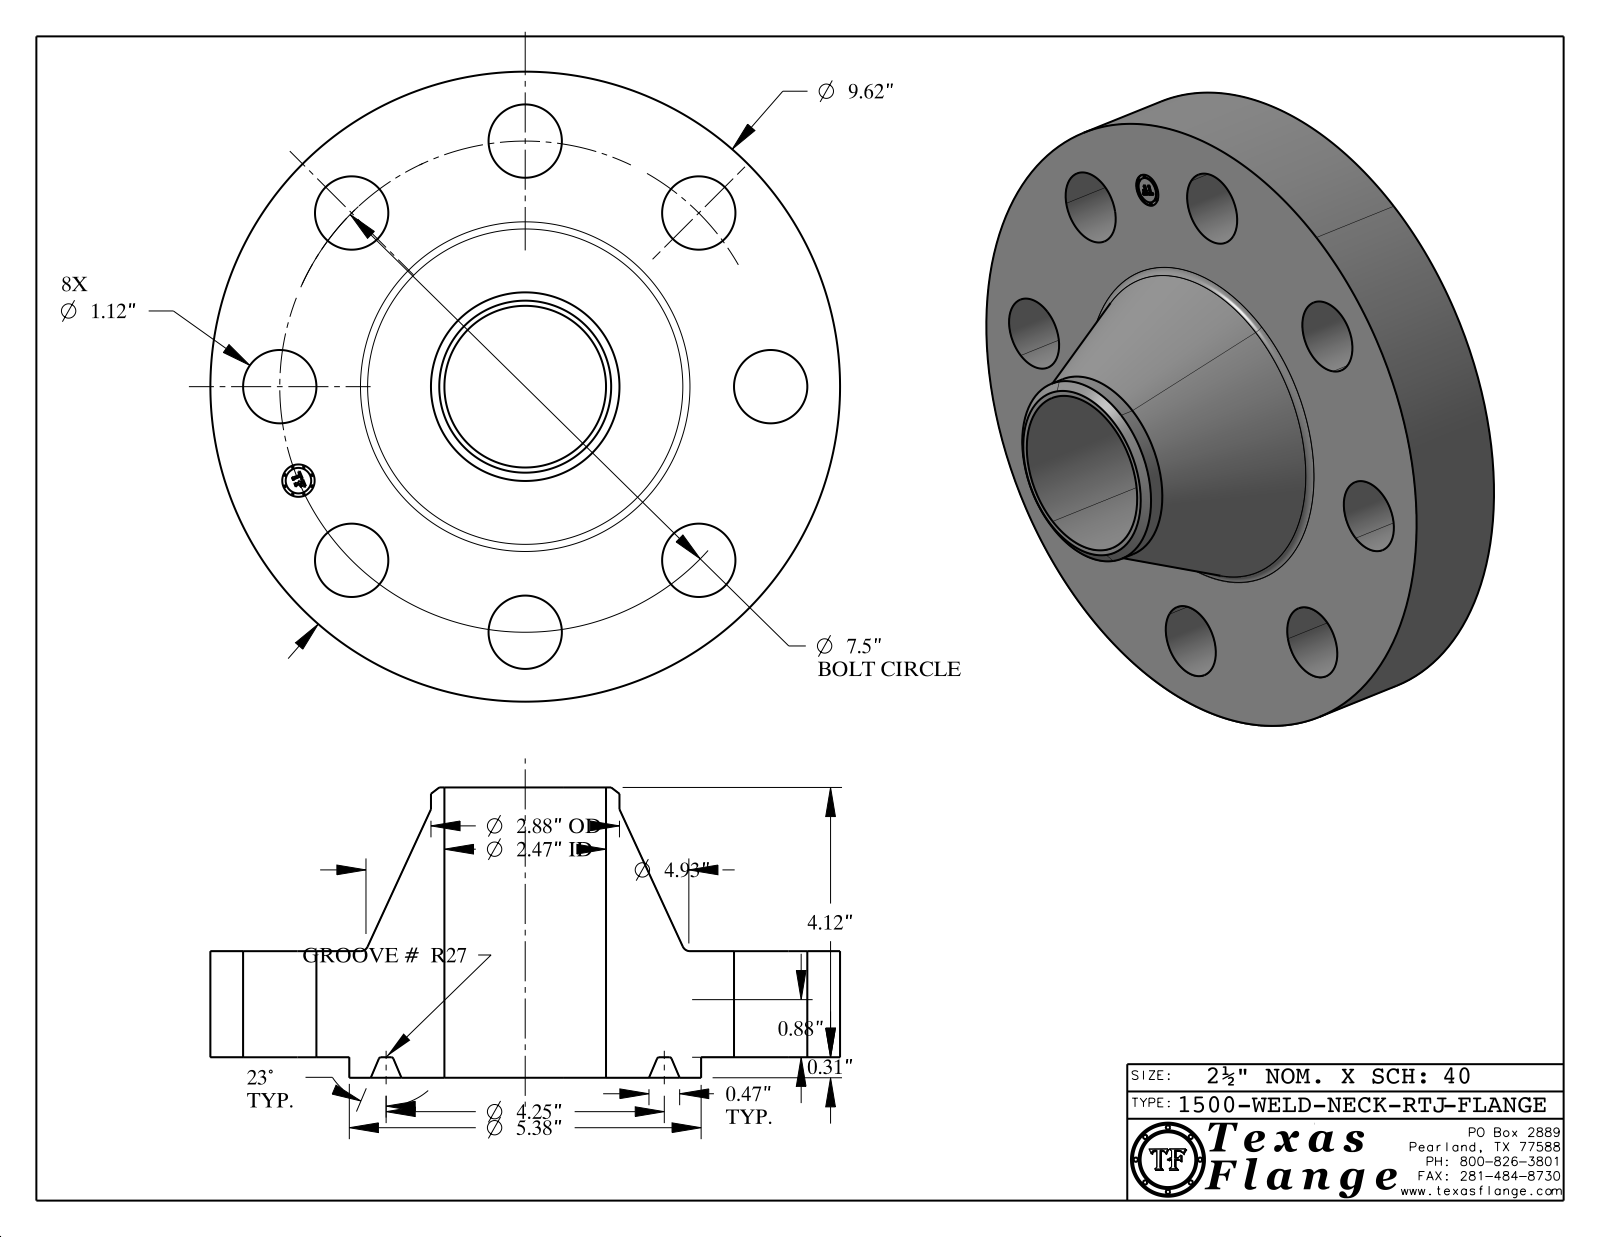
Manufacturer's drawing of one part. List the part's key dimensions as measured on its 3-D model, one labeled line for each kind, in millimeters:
Part name (STEP PRODUCT): 1500-WELD-NECK-RTJ
STEP written by: CATIA V5 STEP AP214 (AUTOMOTIVE_DESIGN)
Units: millimetres
Bodies: 1 solid, 429 faces (371 planar, 44 cylindrical, 14 other)
Overall size (bounding box): 244.3 × 244.3 × 112.6
Volume: 1 930 000 mm³ · Surface area: 179 900 mm²
Round holes (diameter × count): ⌀28.4 ×8, ⌀12.6 ×1, ⌀62.7 ×1
Round bosses / shafts (diameter × count): ⌀0.8 ×8, ⌀244.3 ×1, ⌀136.5 ×1, ⌀73.2 ×1, ⌀9.9 ×1
Main face-to-face distances: 41.1, 8, 49.1, 112.6, 104.6, 63.5, 0.4, 48.7, 40.8, 63.9
Hole centre spacings: 95.3, 72.9, 134.7, 176, 37.2, 158.4, 186.8, 190.5
